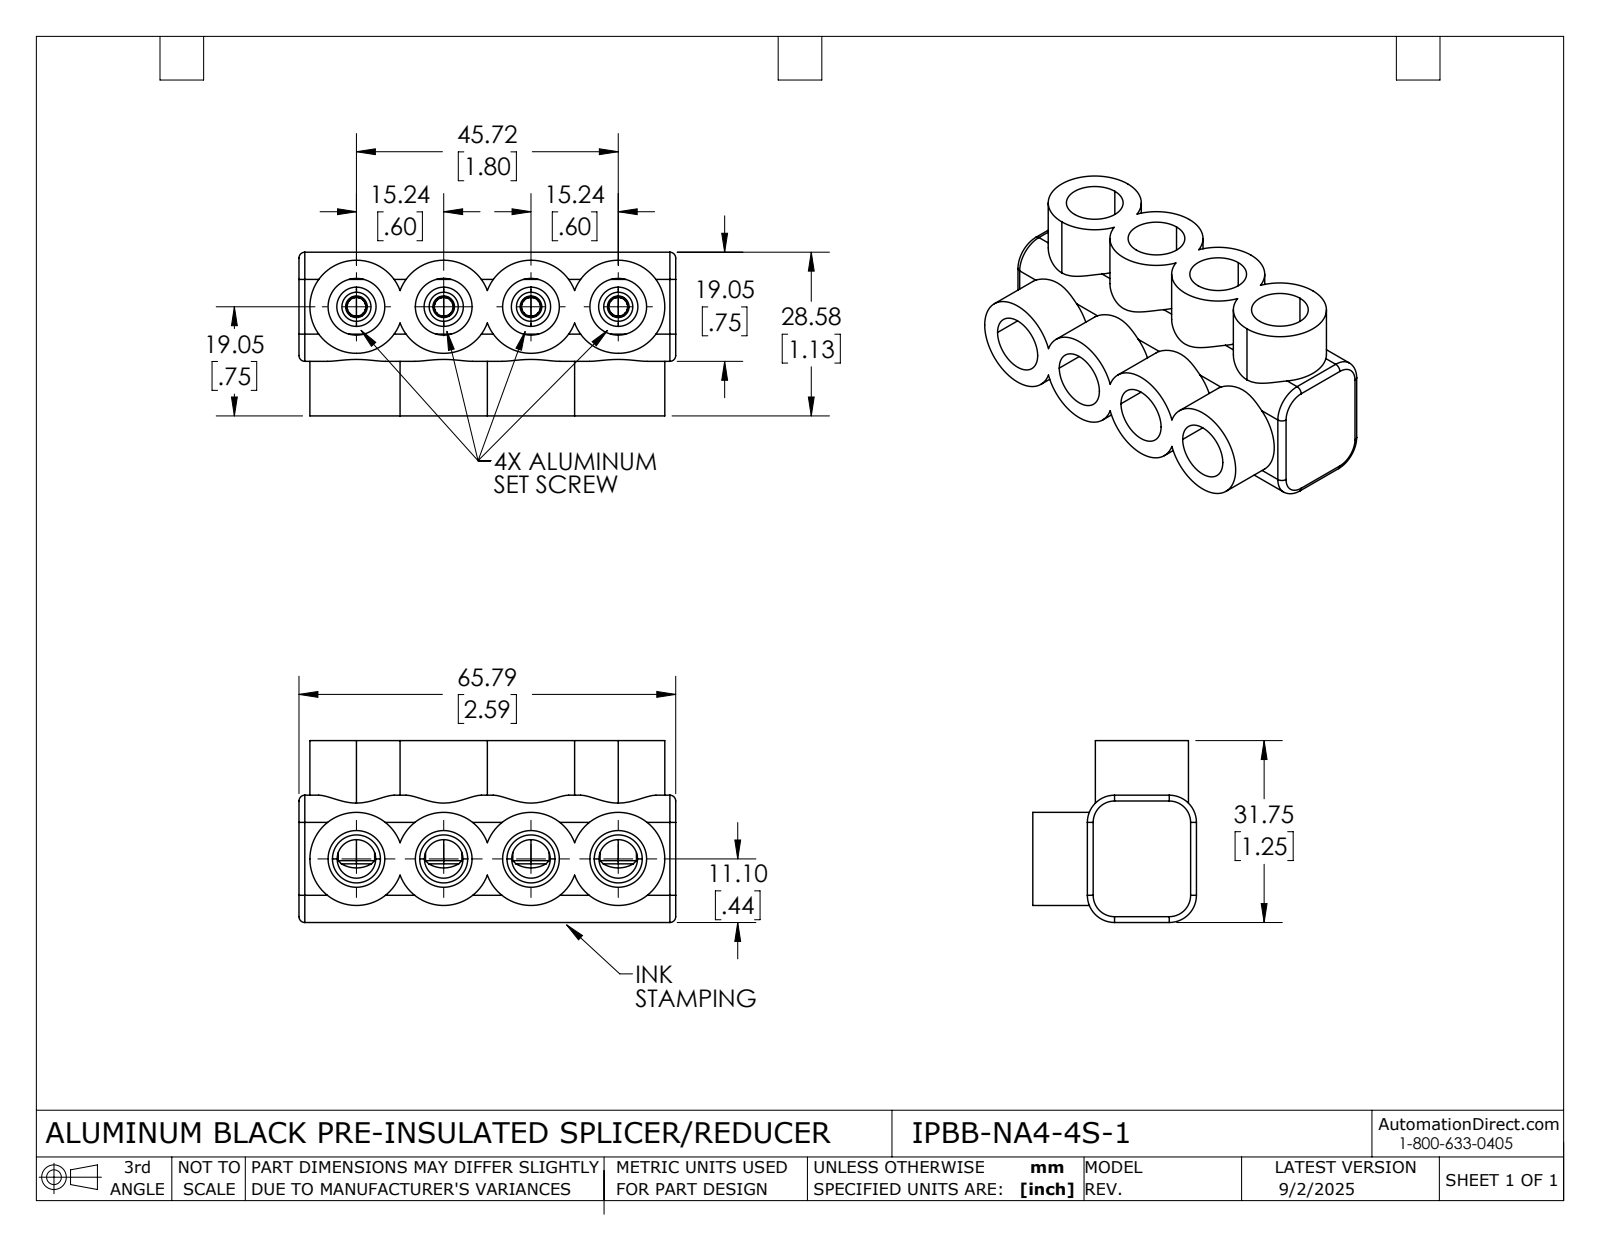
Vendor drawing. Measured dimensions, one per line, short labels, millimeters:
name: IPBB-NA4-4S-1
written by: SolidWorks 2024 (AUTOMOTIVE_DESIGN)
unit: mm
bodies: 6 solids, 289 faces (122 planar, 95 cylindrical, 72 other)
size: 65.8 × 31.8 × 28.6
volume: 32 920 mm³; area: 20 200 mm²
holes: 8× ⌀9.9, 4× ⌀3.3, 4× ⌀5.4, 4× ⌀6.7
bosses: 4× ⌀16.3, 4× ⌀6.4
rounds: 8× R1, 4× R1.6, 4× R4.7, 4× R8.1
face distances: 12.7, 15.9, 3.2, 28.6, 3.2, 62.6, 19.1, 25.4, 31.8, 59.4
hole spacings: 15.2, 30.5, 45.7
